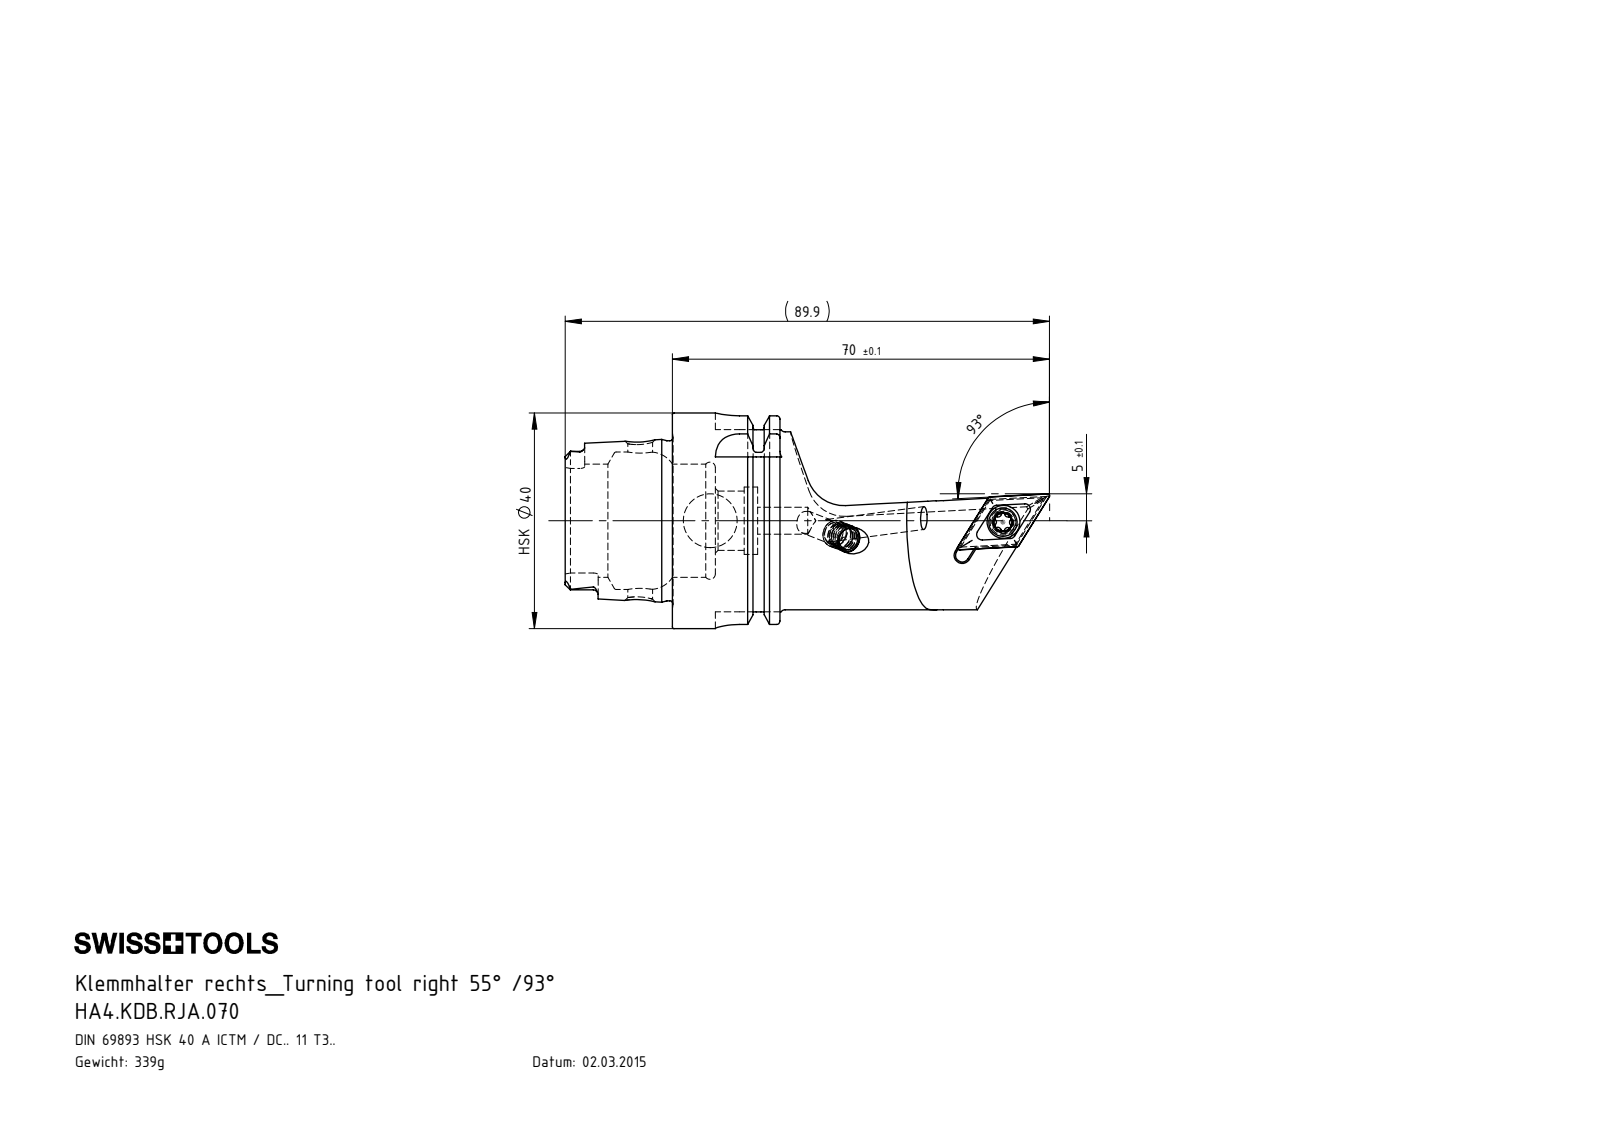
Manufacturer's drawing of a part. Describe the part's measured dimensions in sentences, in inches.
The part is named "DCMT11T304; HA4.KDB.RJA.070; KVT_MB_600_050; HA4-KDB.RJA.070_A_Fertigbearbeitung (+1 more)". Its 3-D file was written by "SolidWorks 2022 (AUTOMOTIVE_DESIGN)". It is 5 solids with 309 faces: 80 planar, 89 cylindrical and 140 other. Overall it measures 3.54 by 1.575 by 1.575 inches. Its volume is 2.621 cubic inches and its surface area 22.11 square inches. Round holes: 2 of diameter 0.165, 2 of diameter 0.197, 1 of diameter 0.13, 1 of diameter 0.157, 1 of diameter 0.173, 1 of diameter 0.181, 1 of diameter 0.24, 1 of diameter 0.394, 1 of diameter 0.433, 1 of diameter 0.492, 1 of diameter 0.827, 1 of diameter 1.004. Round bosses or shafts: 1 of diameter 1.575, 1 of diameter 1.368, 1 of diameter 1.299, 1 of diameter 1.17, 1 of diameter 0.207, 1 of diameter 0.197, 1 of diameter 0.157. Partial cylindrical surfaces (rounded edges, fillets, slot ends): 6 of radius 0.013, 6 of radius 0.023, 6 of radius 0.035, 4 of radius 0.177, 2 of radius 0.072, 2 of radius 0.074, 2 of radius 0.276, 1 of radius 0.049. The main face-to-face distances are 0.313, 0.785, 0.472, 0.144, 0.783, 1.096, 1.569, 1.406, 0.622, 0.309. The hole center spacings are 2.14, 2.144.
